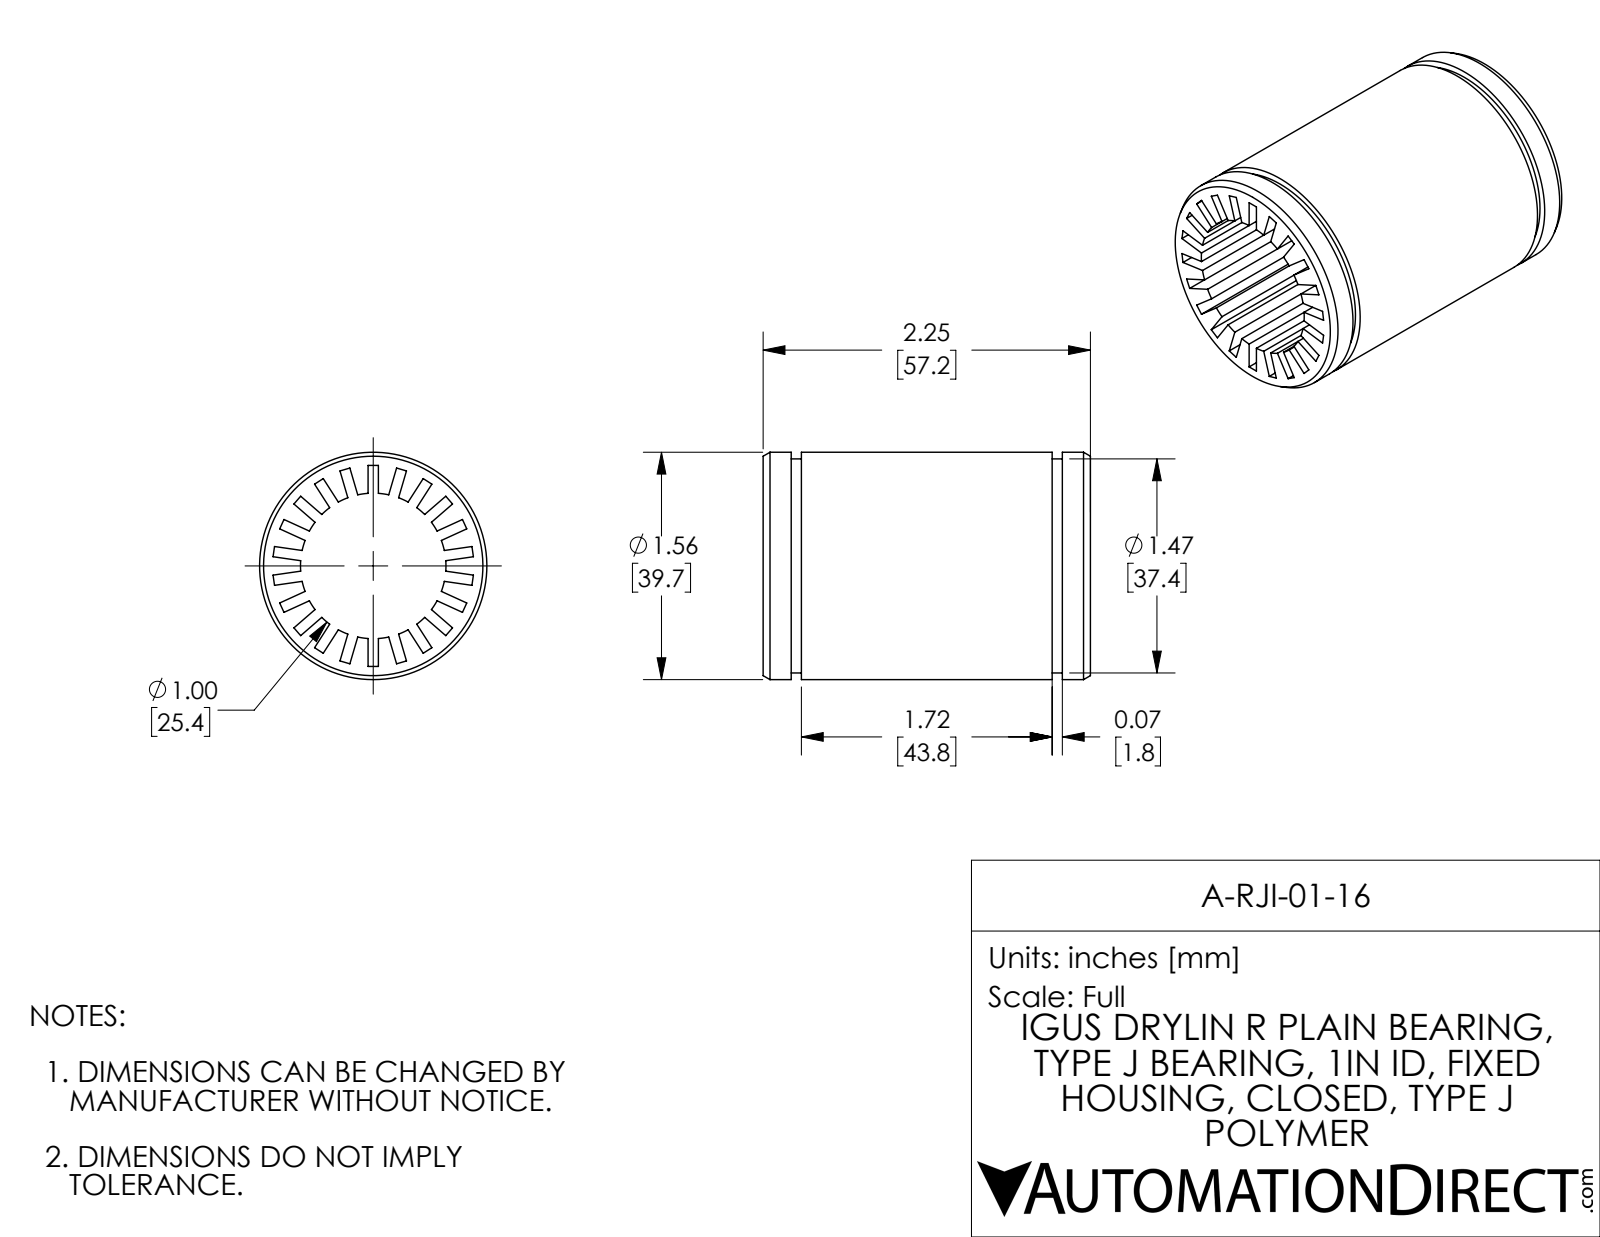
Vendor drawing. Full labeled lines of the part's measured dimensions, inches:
Part name (STEP PRODUCT): A-RJI-01-16
STEP written by: SolidWorks 2017 (AUTOMOTIVE_DESIGN)
Units: inches
Bodies: 1 solid, 108 faces (72 planar, 32 cylindrical, 4 other)
Overall size (bounding box): 2.25 × 1.563 × 1.563
Volume: 1.84 in³ · Surface area: 39.41 in²
Round bosses / shafts (diameter × count): ⌀1.563 ×1, ⌀1.471 ×1
Partial cylindrical surfaces — rounded edges, fillets, slot ends (radius × count): R0.5 ×1
Main face-to-face distances: 0.071, 1.382, 1.381, 2.25, 0.193, 0.263, 1.987, 2.057, 1.794, 0.07
